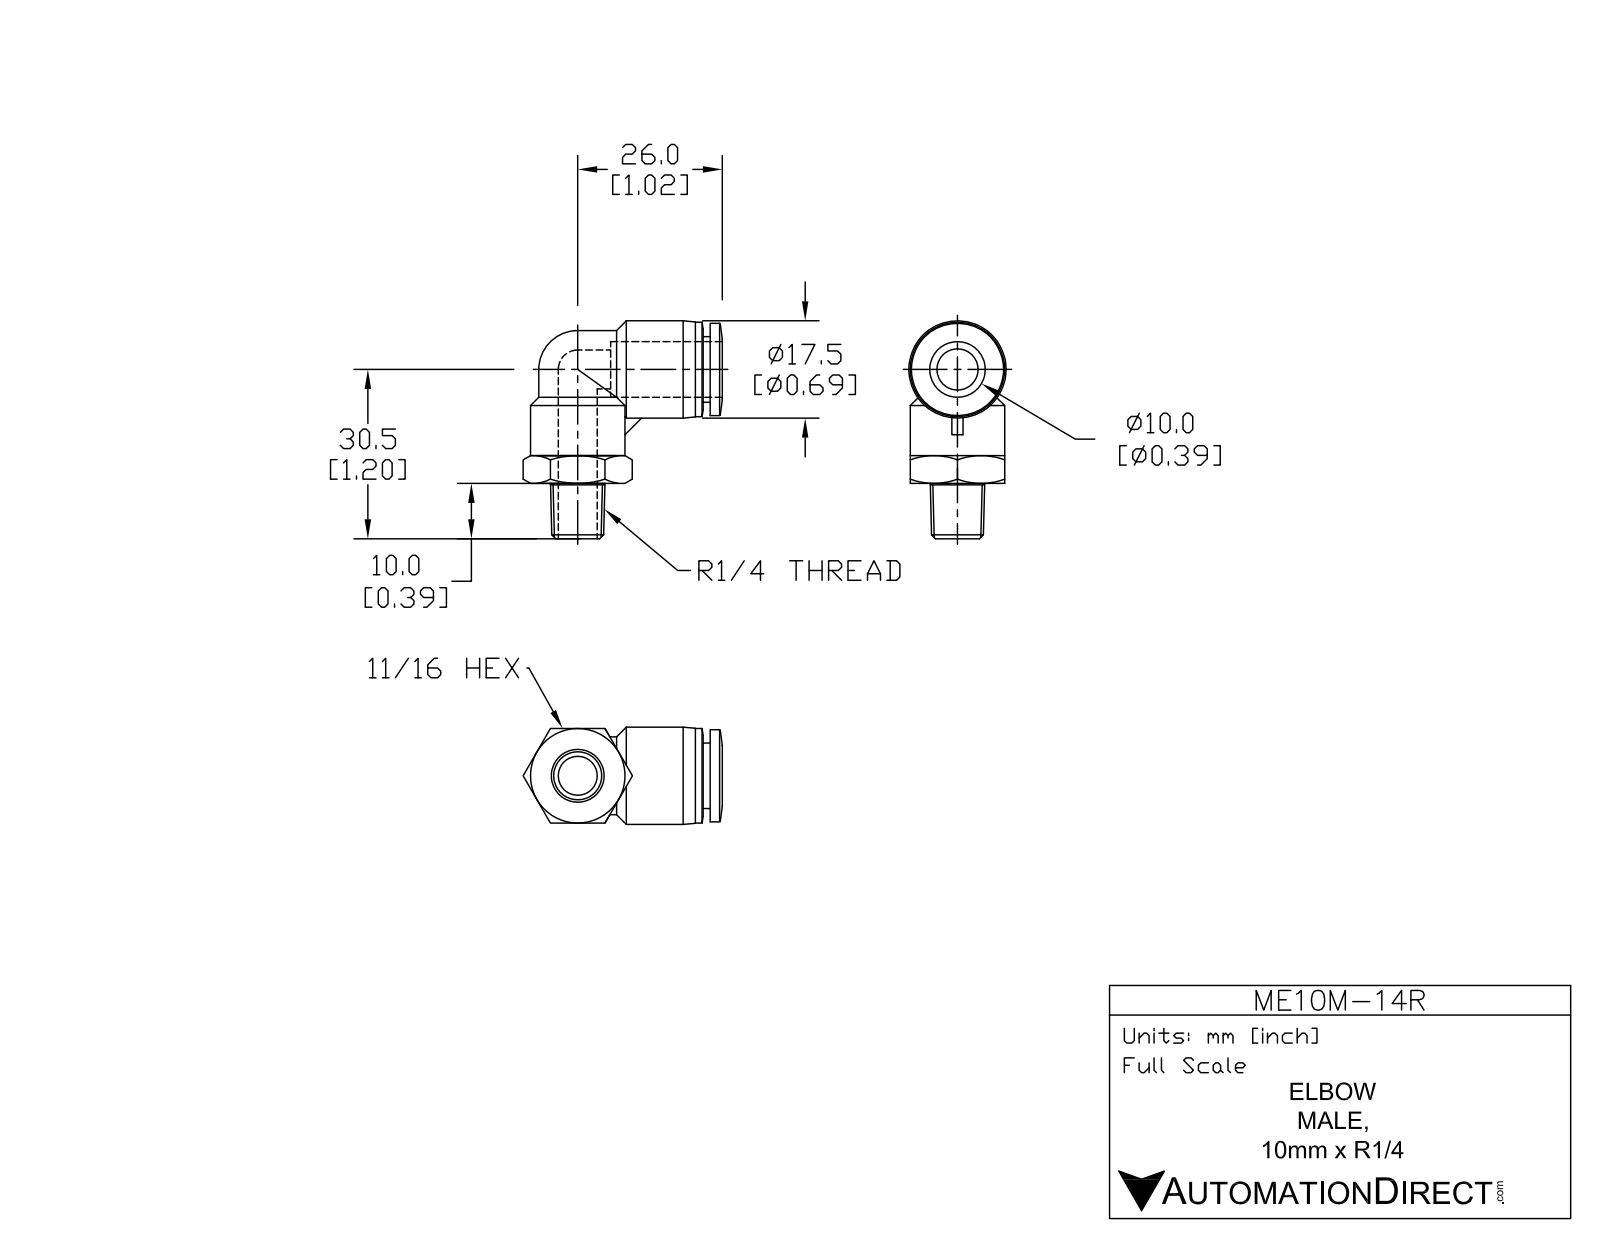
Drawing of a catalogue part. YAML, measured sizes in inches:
part_name: "ME10M-14R"
step_written_by: "SolidWorks 2015 (AUTOMOTIVE_DESIGN)"
units: inches
bodies: {solids: 1, faces: 71, planar: 16, cylindrical: 20, other: 35}
overall_size: [1.585, 1.355, 0.689]
volume: 0.444
surface_area: 7.485
round_holes:
  - {diameter: 0.315, count: 2}
  - {diameter: 0.406, count: 1}
round_bosses_or_shafts:
  - {diameter: 0.669, count: 2}
  - {diameter: 0.689, count: 1}
  - {diameter: 0.654, count: 1}
  - {diameter: 0.551, count: 1}
  - {diameter: 0.465, count: 1}
partial_cylinders:
  - {radius: 0.276, count: 1}
face_to_face_distances: [0.669, 0.049, 0.394, 0.659, 0.709, 0.295, 0.374, 0.079, 0.604, 0.055]
